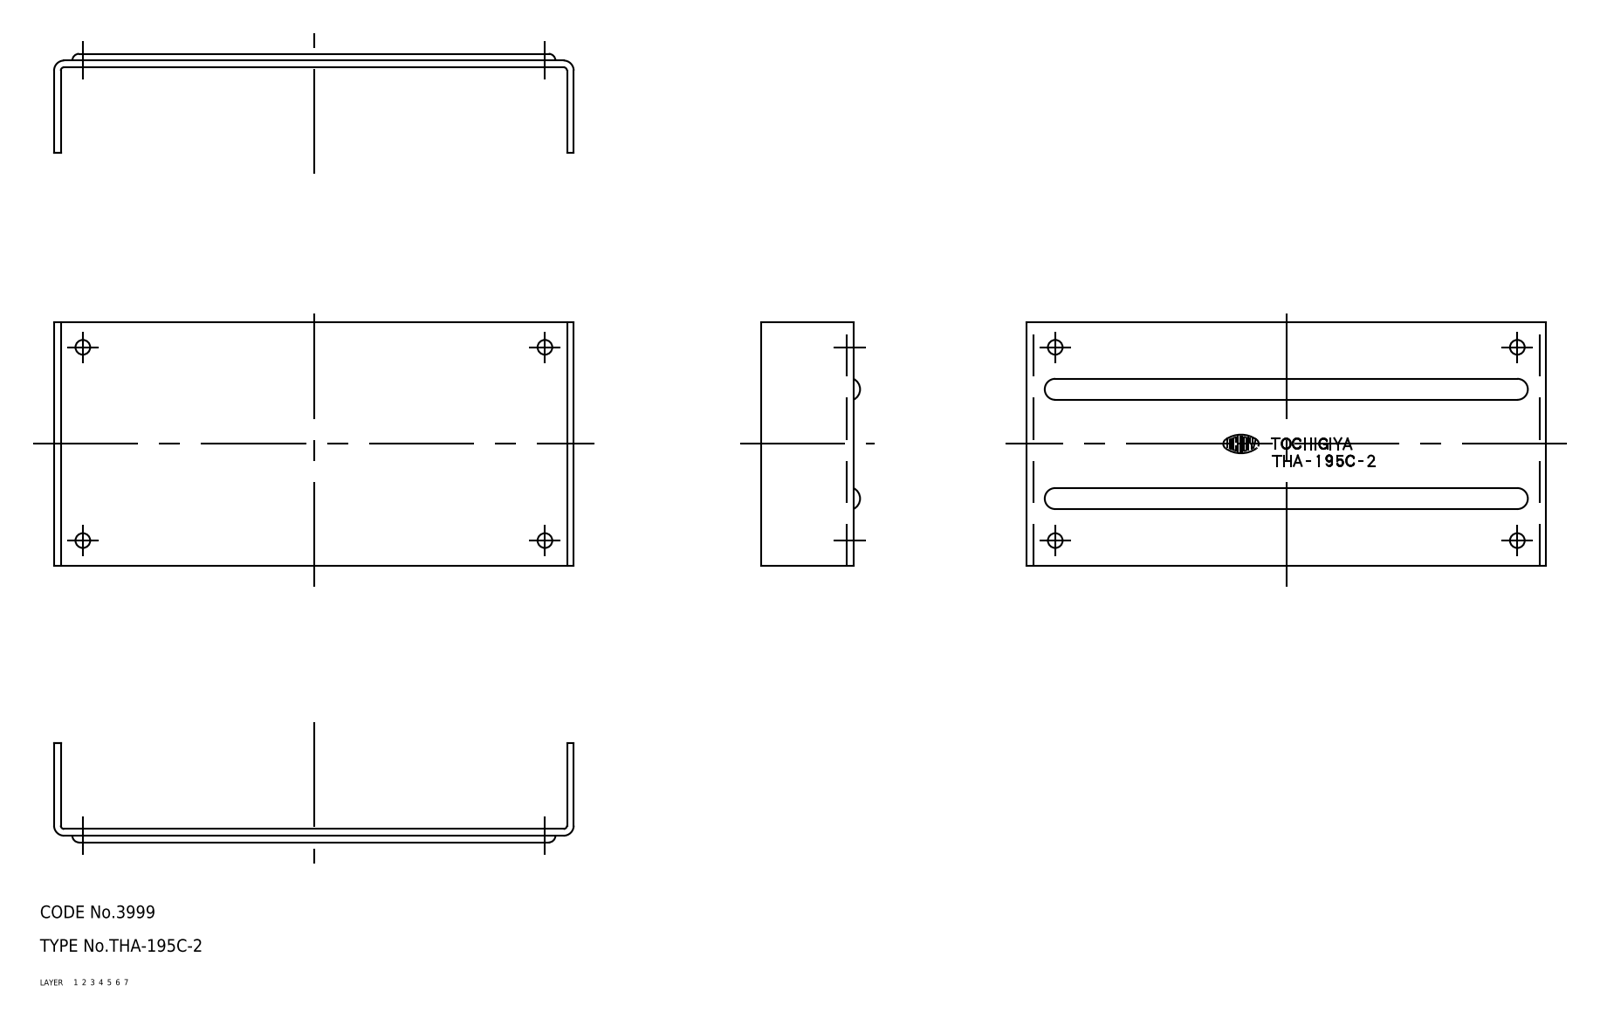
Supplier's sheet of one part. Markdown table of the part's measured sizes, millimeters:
| quantity | value |
| --- | --- |
| part name | bracket |
| STEP written by | CADfix (AUTOMOTIVE_DESIGN) |
| units | millimeters |
| bodies | 1 solid, 48 faces (0 planar, 0 cylindrical, 48 other) |
| overall size | 123.7 × 58 × 23.6 |
| volume | 16 386 mm³ |
| surface area | 19 927 mm² |
